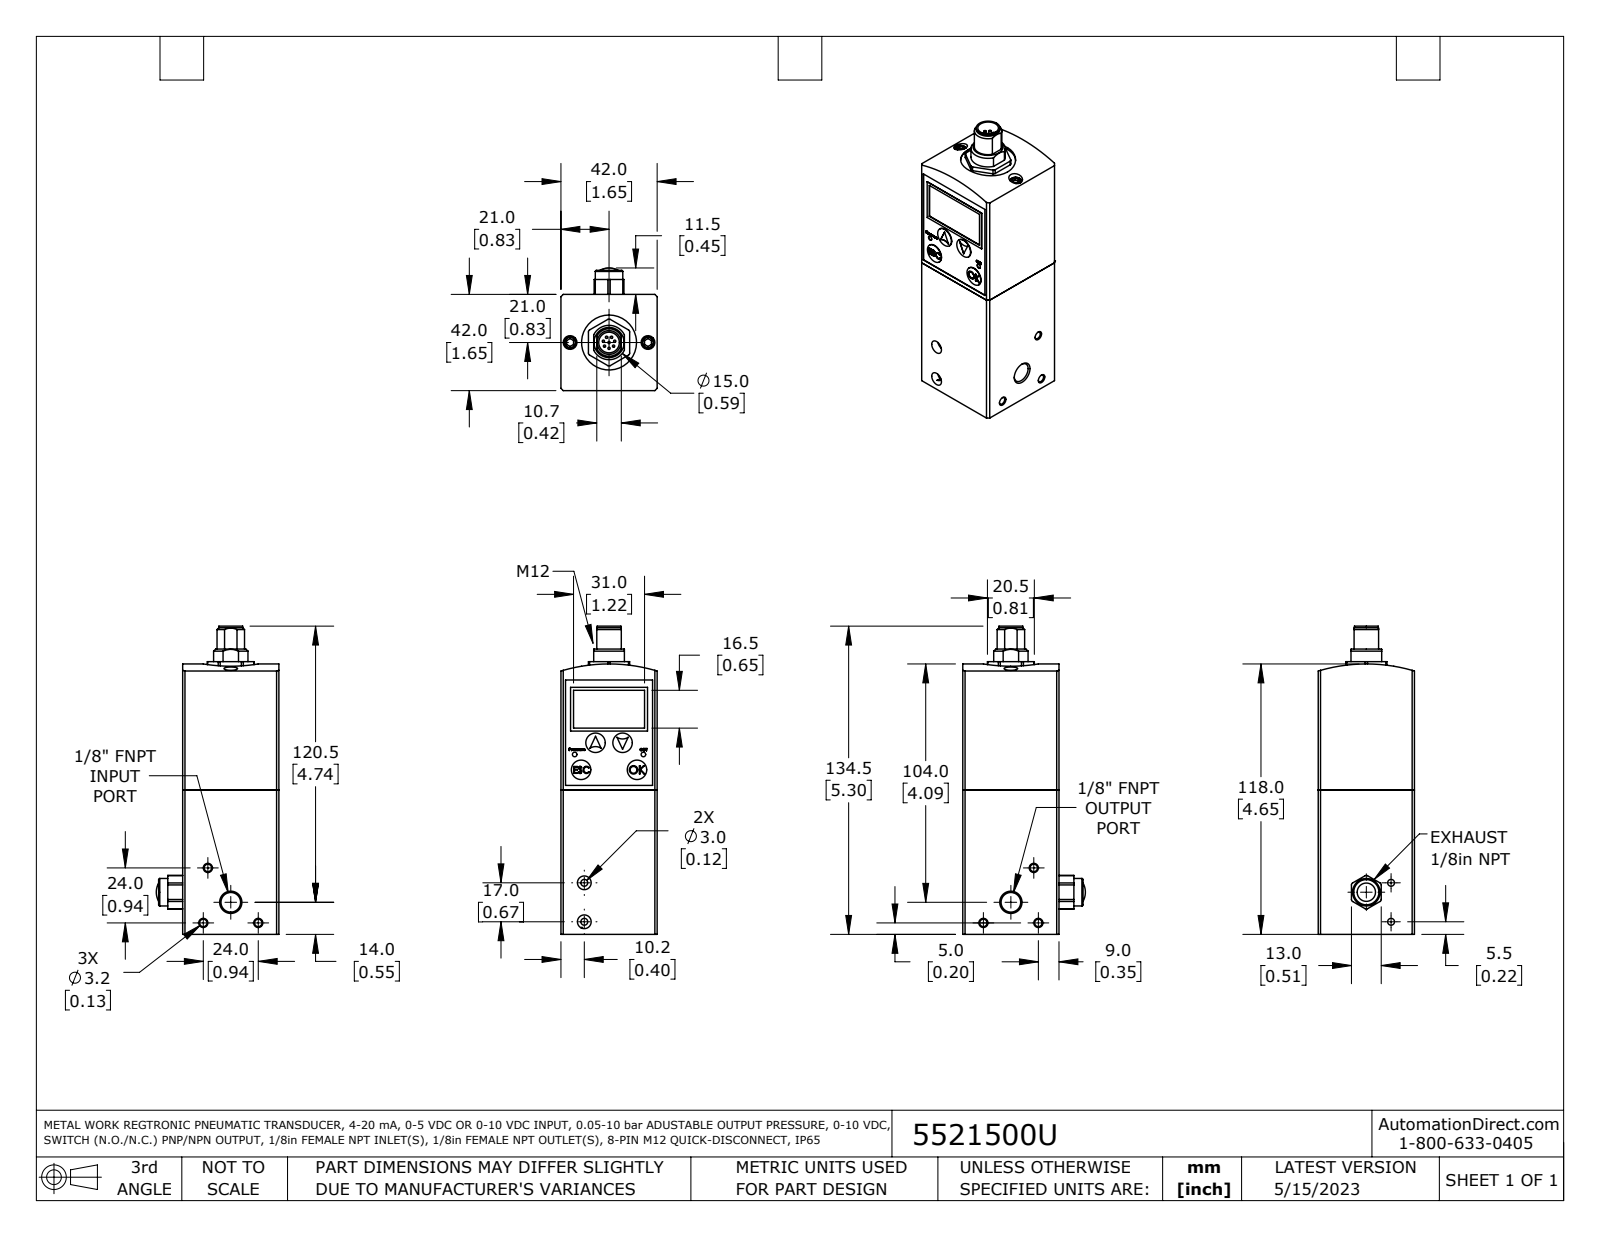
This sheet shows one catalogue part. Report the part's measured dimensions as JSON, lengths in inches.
{"part_name": "5521500U", "step_written_by": "SolidWorks 2021 (AUTOMOTIVE_DESIGN)", "units": "inches", "bodies": {"solids": 1, "faces": 538, "planar": 243, "cylindrical": 248, "other": 47}, "overall_size": [5.295, 2.107, 1.654], "volume_in3": 12.61, "surface_area_in2": 41.89, "round_holes": [[0.236, 8], [0.128, 3], [0.03, 2], [0.079, 2], [0.118, 2], [0.041, 1], [0.145, 1], [0.337, 1], [0.354, 1], [0.945, 1]], "round_bosses_or_shafts": [[0.039, 8], [0.197, 6], [0.335, 4], [0.023, 2], [0.472, 1], [0.409, 1], [0.117, 1], [0.033, 1]], "partial_cylinders_radius": [[0.039, 12], [0.006, 4], [0.009, 3], [0.004, 2], [0.004, 2], [0.005, 2], [0.005, 2], [0.007, 2]], "face_to_face_distances": [1.654, 1.646, 0.016, 1.638, 2.283, 2.48, 1.653, 0.015, 0.079, 0.276], "hole_center_spacings": [0.676, 0.882, 1.413, 0.669, 1.339, 0.591, 1.15, 1.765]}
